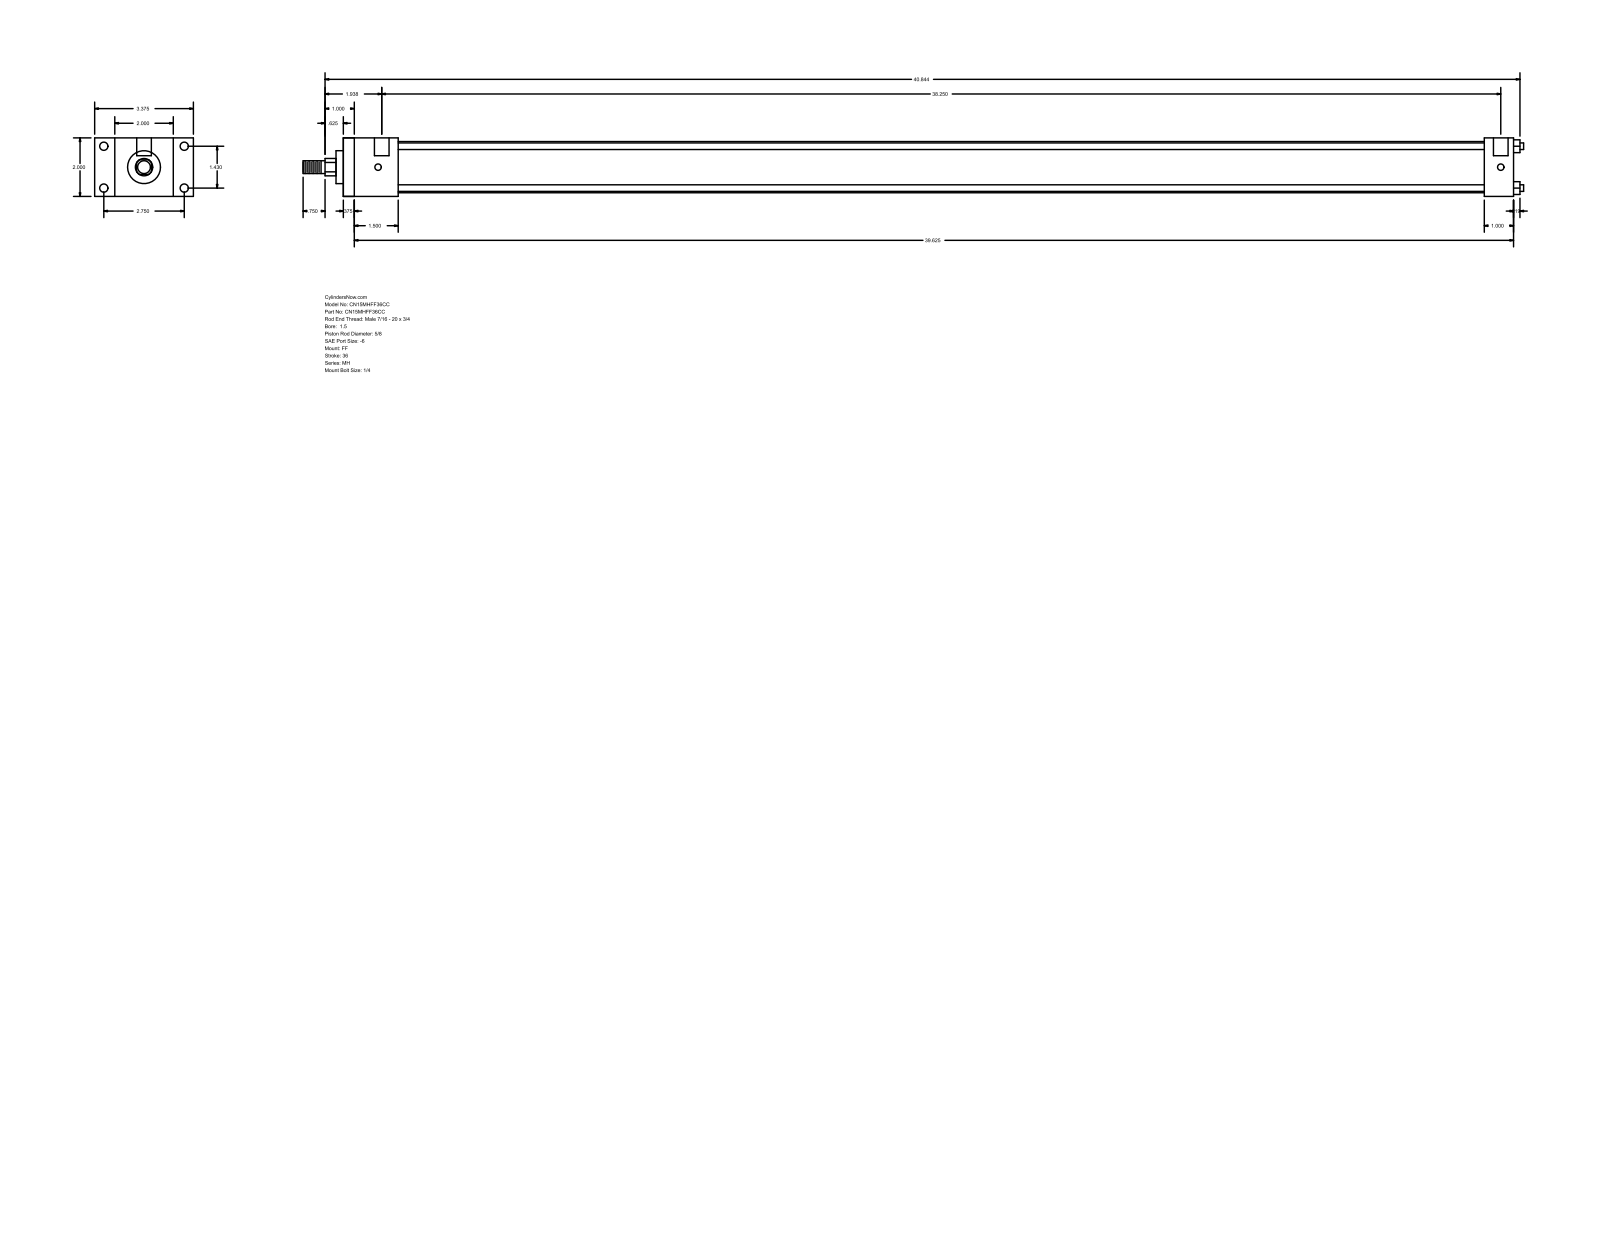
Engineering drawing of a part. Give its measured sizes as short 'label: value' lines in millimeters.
name: MH_FF__0150_0.625
written by: GSSL Pune (CONFIG_CONTROL_DESIGN)
unit: mm
bodies: 0 solids, 92 faces (64 planar, 28 cylindrical, 0 other)
size: 1059.66 × 85.72 × 50.8
holes: 4× ⌀5.56, 4× ⌀7.14, 2× ⌀12.7
bosses: 4× ⌀5.71, 1× ⌀44.45, 1× ⌀28.57, 1× ⌀15.88, 1× ⌀11.11
rounds: 1× R7.54
face distances: 50.8, 1016, 1006.48, 9.52, 25.4, 17.46, 68.26, 47.62, 38.1, 968.38
hole spacings: 36.32, 69.84, 78.72, 974.72, 3.17, 971.55
